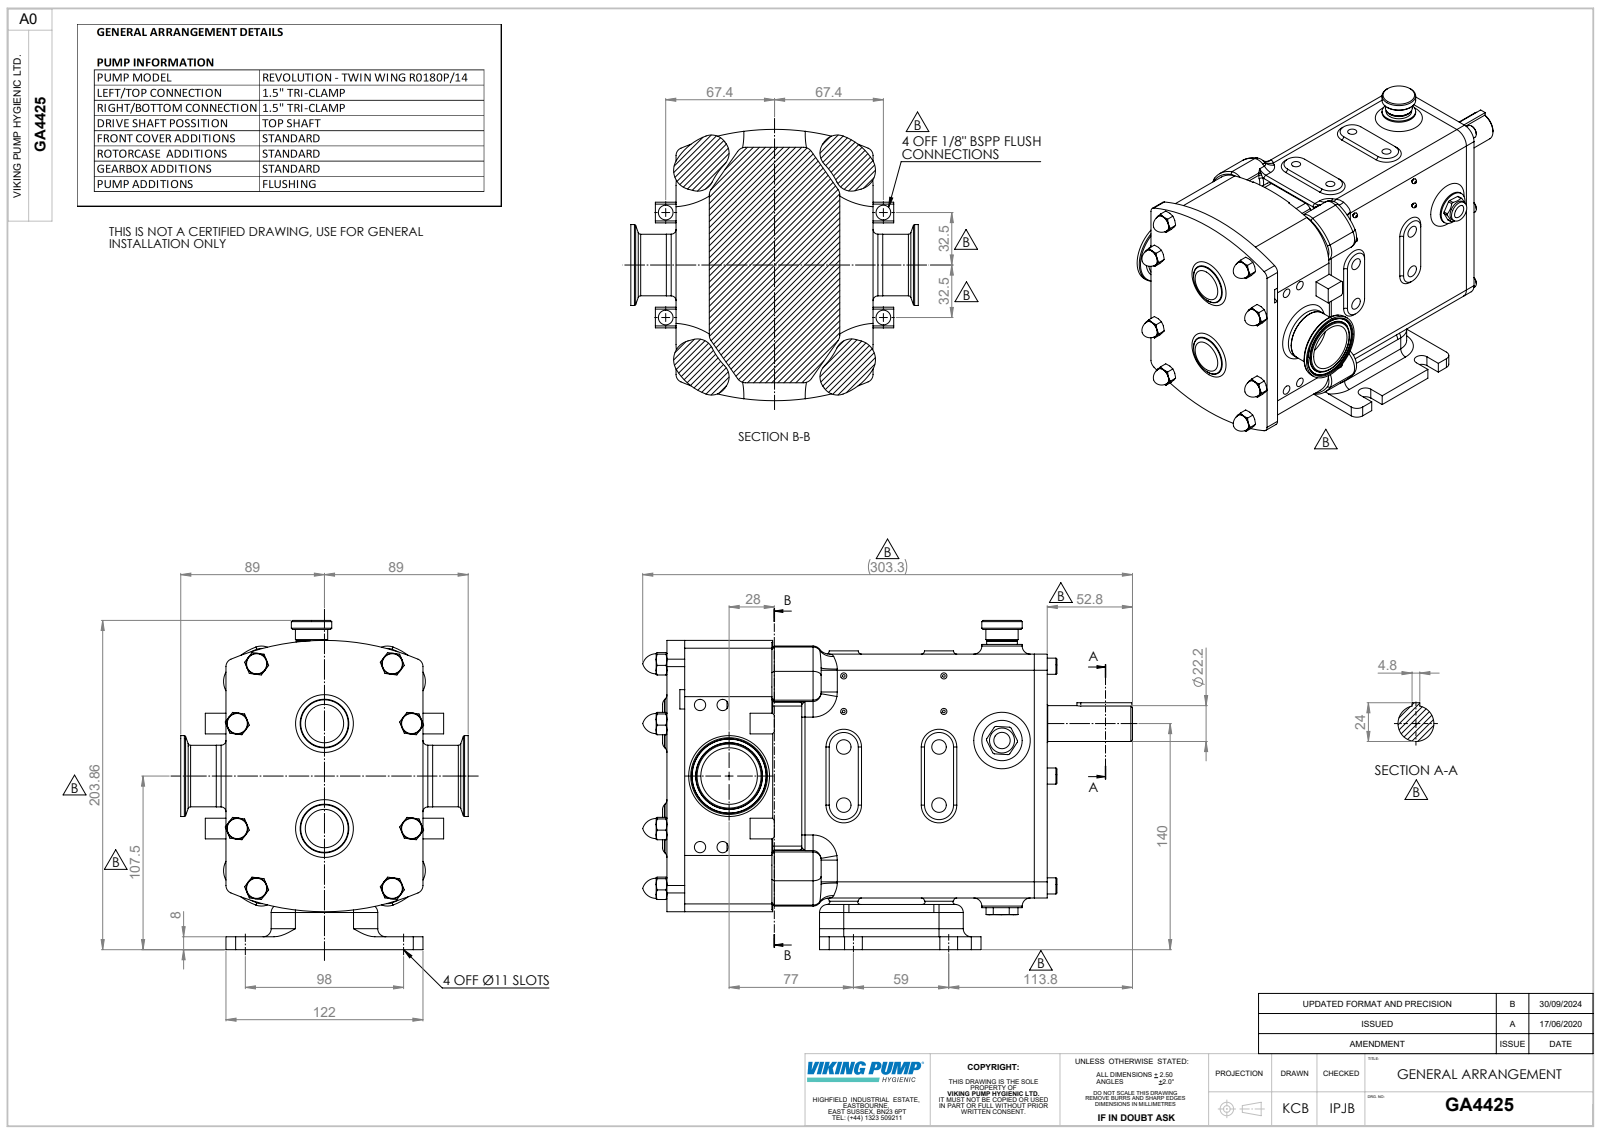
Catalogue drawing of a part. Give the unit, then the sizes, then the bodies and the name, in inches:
Units: inches
Overall size (bounding box): 11.941 × 8.026 × 7.008
Round holes (diameter × count): ⌀0.268 ×4, ⌀0.276 ×4, ⌀0.354 ×4, ⌀0.358 ×4, ⌀0.22 ×2, ⌀0.433 ×2, ⌀0.887 ×1, ⌀1.38 ×1
Round bosses / shafts (diameter × count): ⌀0.394 ×6, ⌀0.984 ×4, ⌀0.512 ×4, ⌀0.383 ×2, ⌀1.972 ×1, ⌀1.504 ×1, ⌀1.5 ×1, ⌀0.985 ×1
Partial cylindrical surfaces — rounded edges, fillets, slot ends (radius × count): R0.079 ×28, R0.394 ×26, R0.197 ×19, R0.236 ×14, R0.315 ×8, R0.05 ×6, R0.049 ×4, R0.217 ×4
Main face-to-face distances: 3.386, 0.709, 9.272, 4.094, 0.236, 0.945, 0.866, 7.205, 0.079, 4.803
Hole centre spacings: 1.417, 2.323, 2.721, 2.559, 0.551, 1.048, 1.502, 1.563
Volume: 225.5 in³ · Surface area: 385.8 in²
Bodies: 7 solids, 1331 faces (415 planar, 345 cylindrical, 571 other)
Part name (STEP PRODUCT): Copy of Z94-8613-91^GA4425; Copy of R0180 CPP H TSD^GA4425; GA4425; Copy of RA94-5121-22M^GA4425
STEP written by: SolidWorks 2023 (AUTOMOTIVE_DESIGN)
